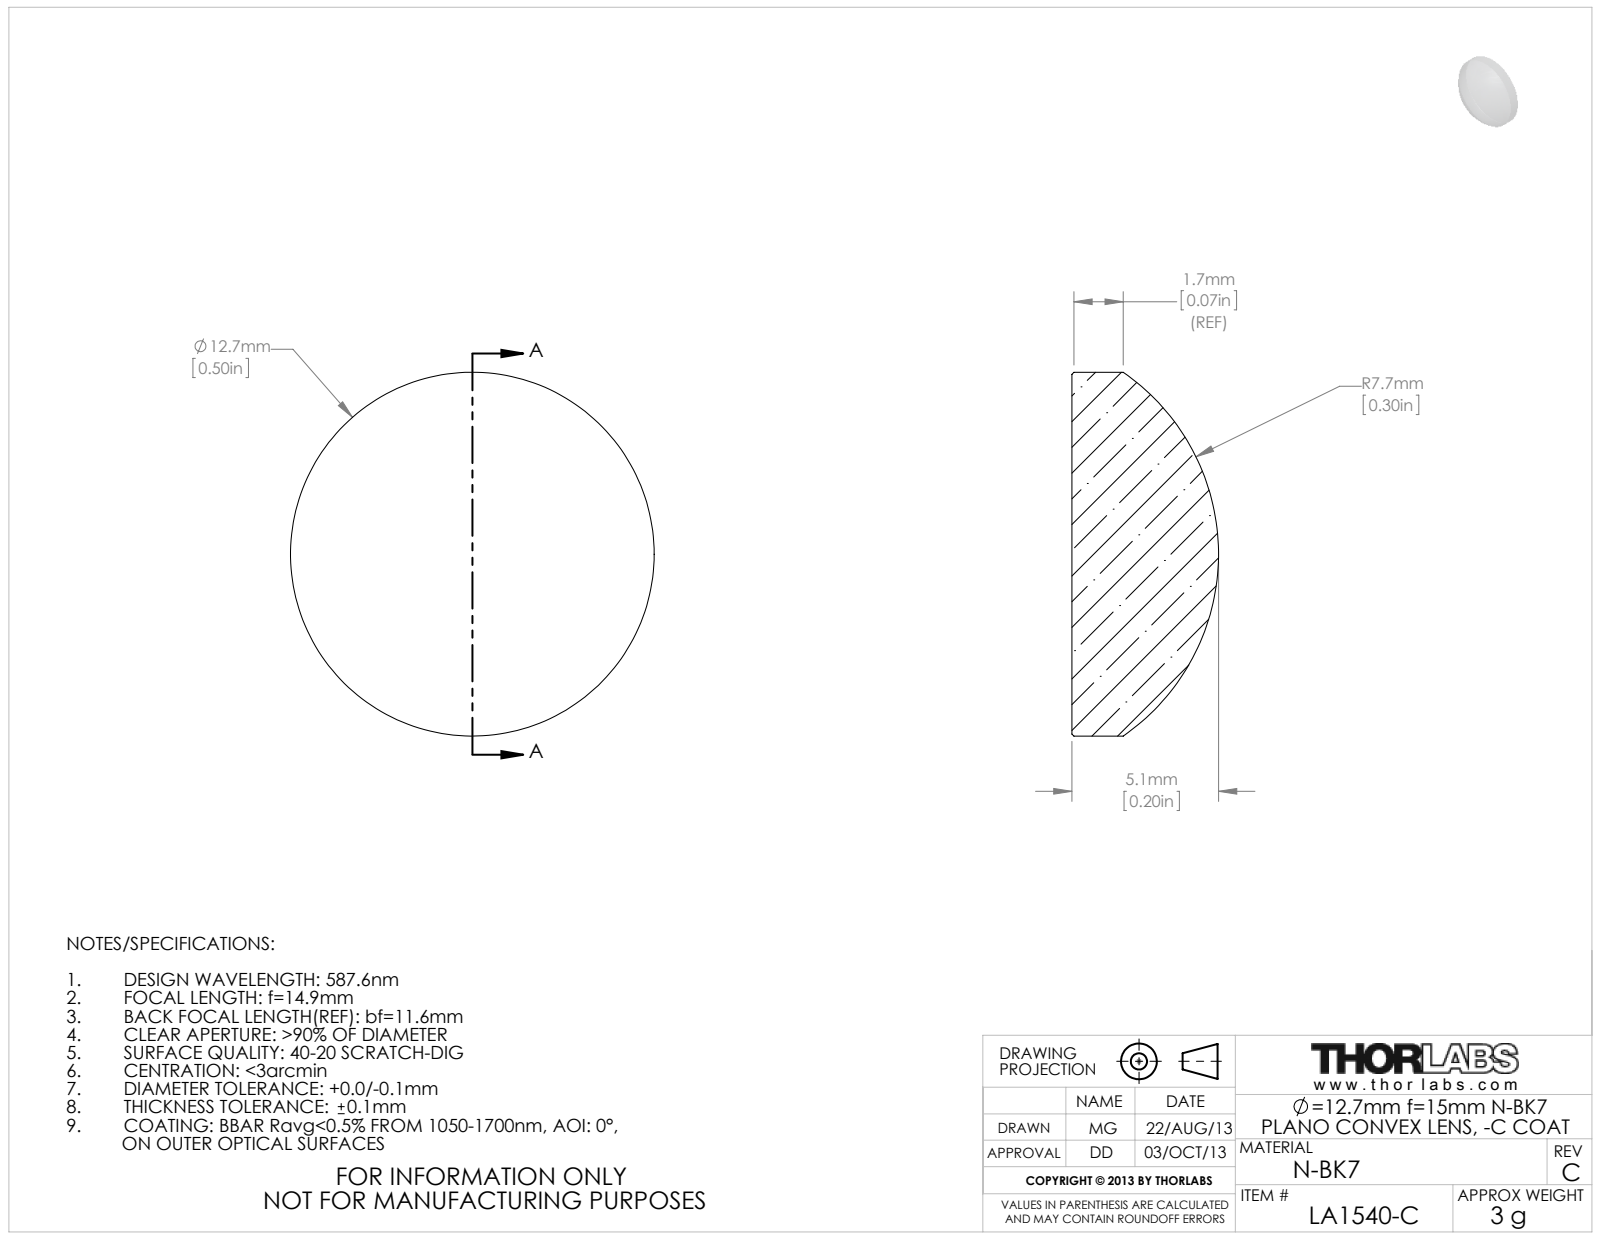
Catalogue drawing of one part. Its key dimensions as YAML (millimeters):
part_name: "4568-E0W"
step_written_by: "SolidWorks 2009 (AUTOMOTIVE_DESIGN)"
units: millimeters
bodies: {solids: 1, faces: 5, planar: 1, cylindrical: 2, other: 2}
overall_size: [12.7, 12.7, 5.12]
volume: 457
surface_area: 360
round_bosses_or_shafts:
  - {diameter: 12.7, count: 1}
